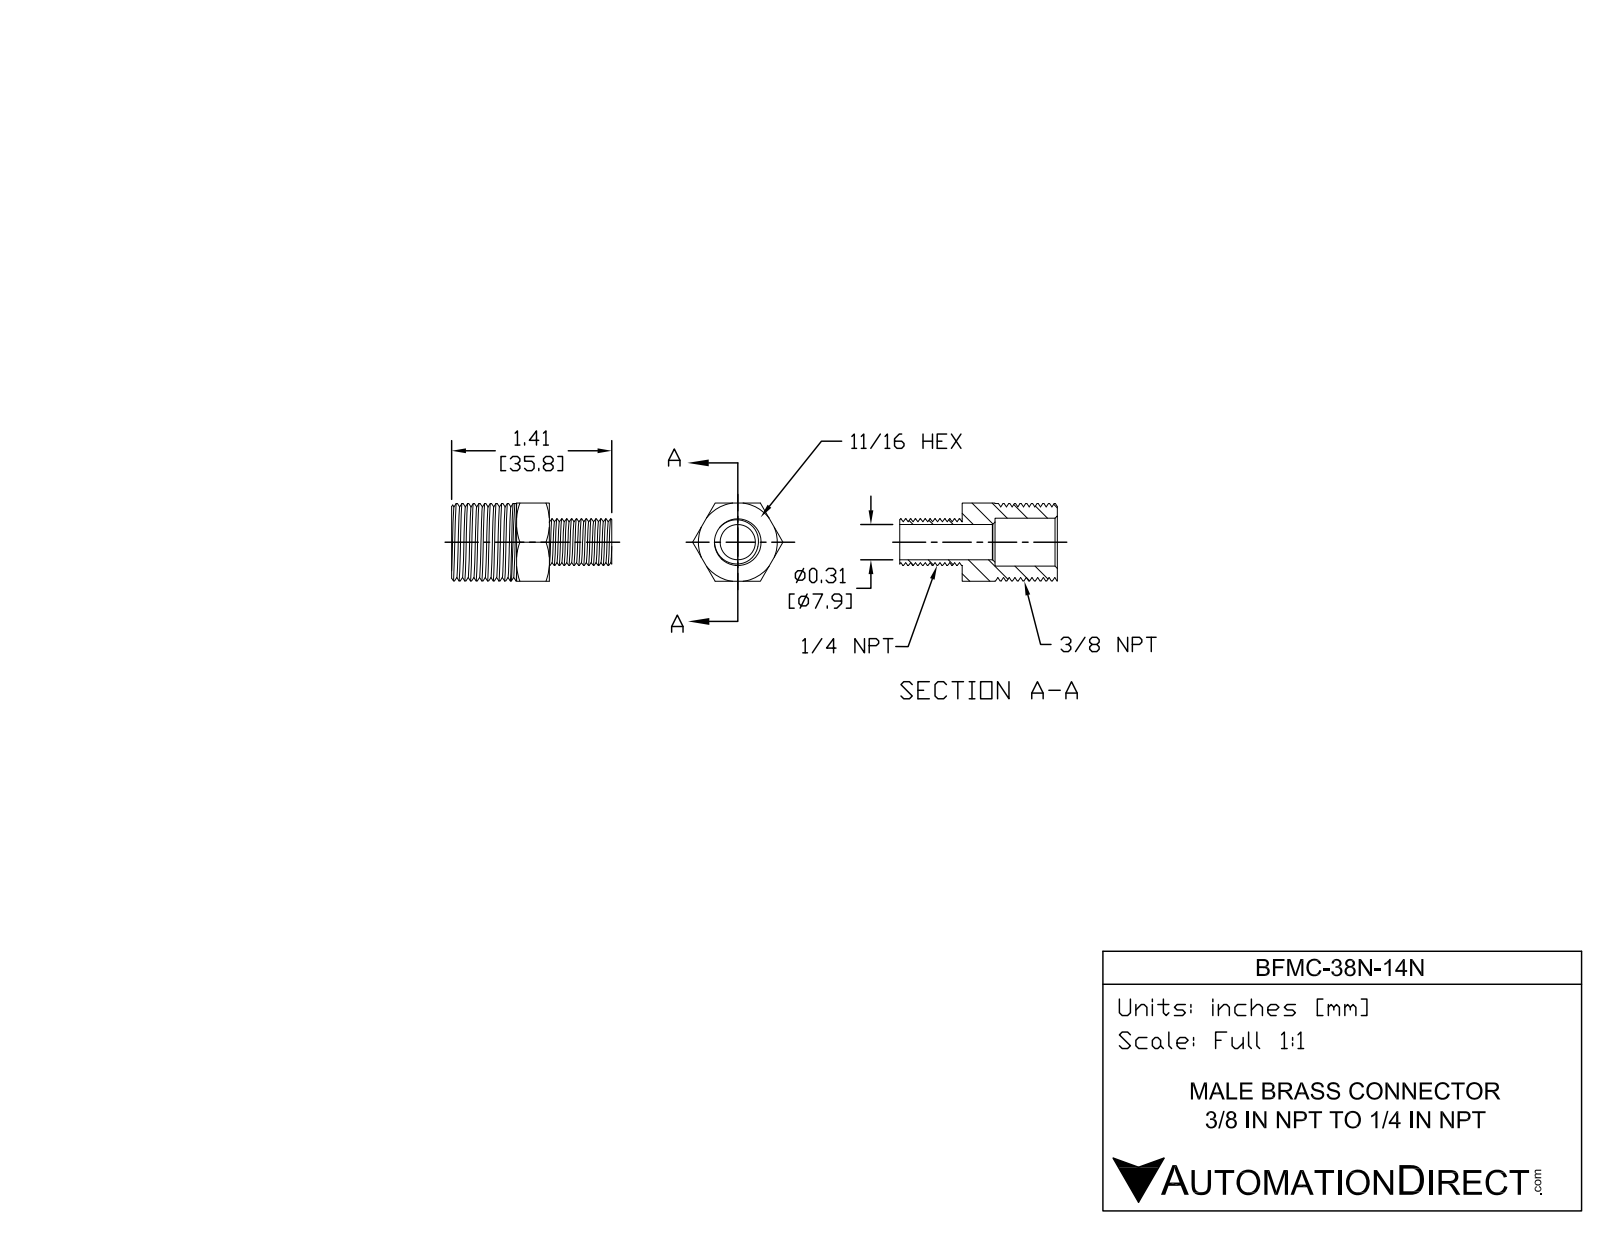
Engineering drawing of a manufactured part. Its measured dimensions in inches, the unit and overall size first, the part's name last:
Units: inches
Overall size (bounding box): 1.385 × 0.794 × 0.688
Round holes (diameter × count): ⌀0.31 ×1, ⌀0.421 ×1
Round bosses / shafts (diameter × count): ⌀0.68 ×1, ⌀0.41 ×1
Main face-to-face distances: 0.687, 0.836, 0.548, 0.288, 1.385, 0.837, 0.549, 0.344
Volume: 0.227 in³ · Surface area: 5.904 in²
Bodies: 1 solid, 89 faces (14 planar, 53 cylindrical, 22 other)
Part name (STEP PRODUCT): BFMC-38N-14N
STEP written by: SolidWorks 2015 (CONFIG_CONTROL_DESIGN)
